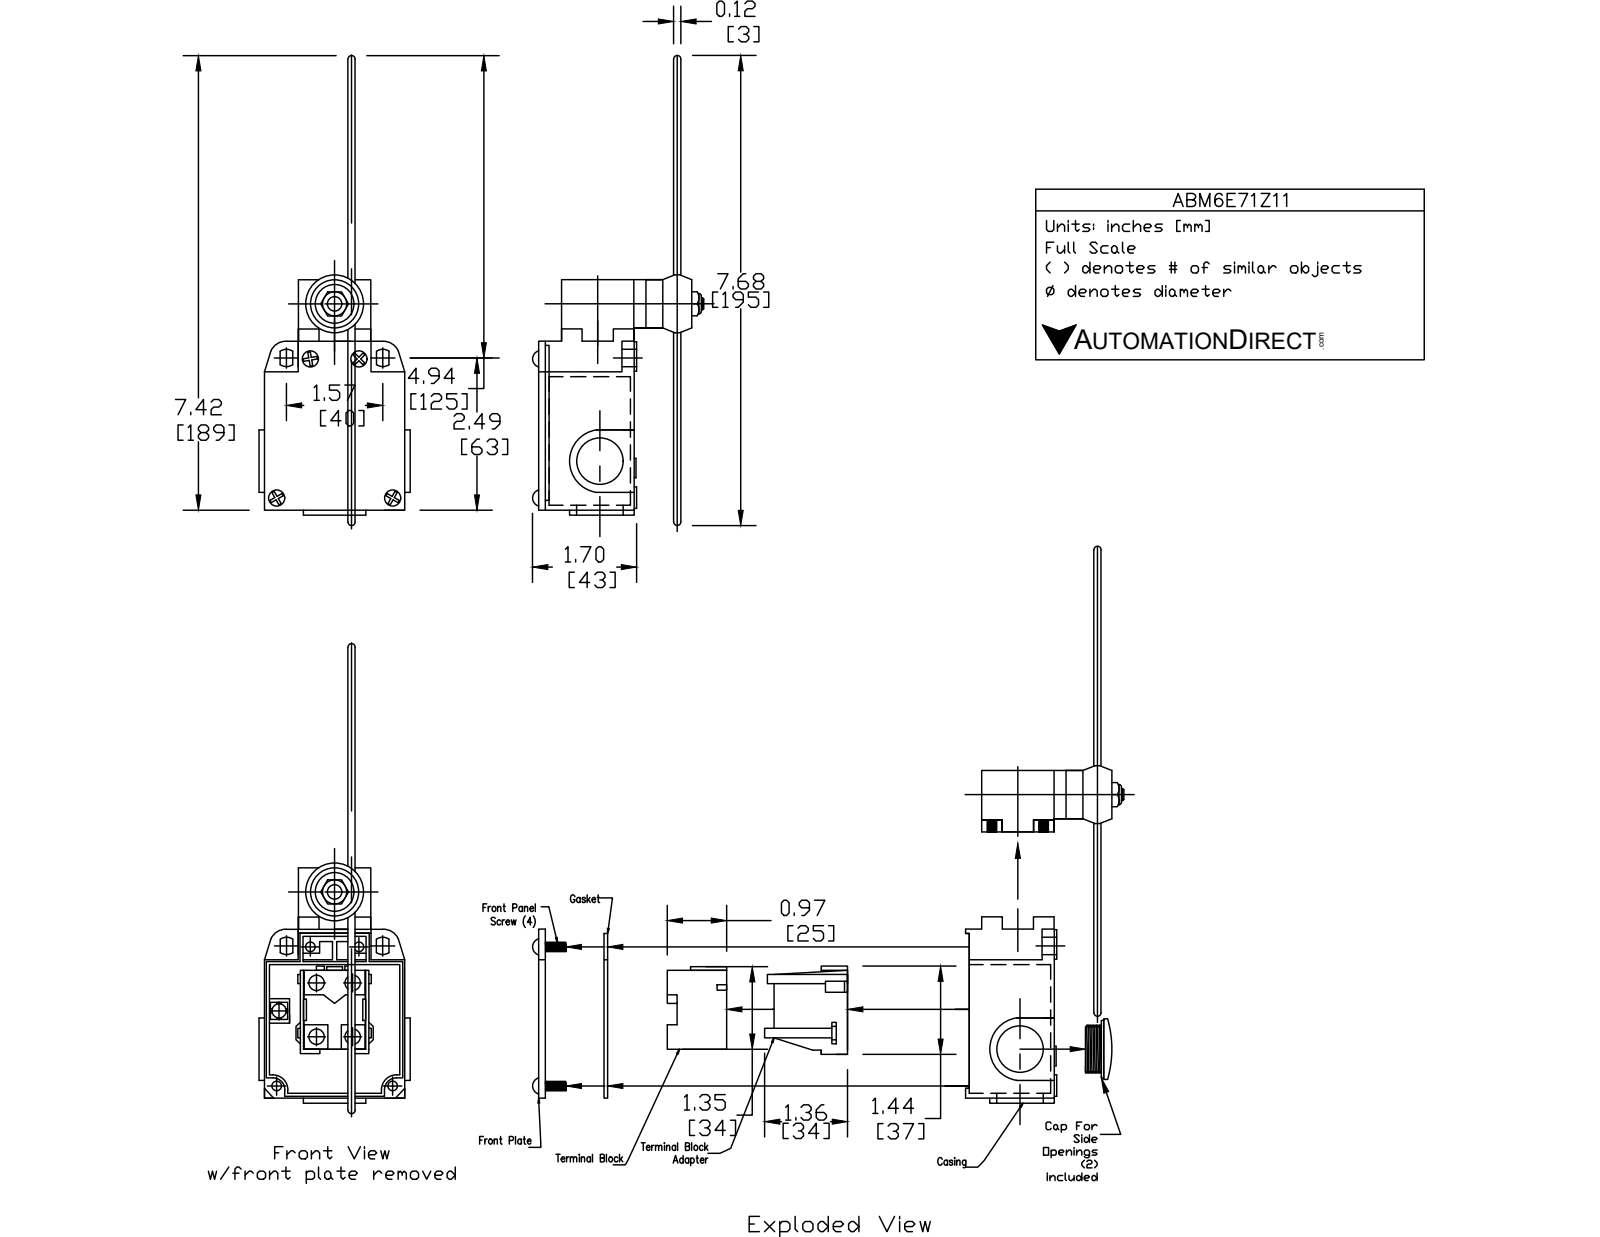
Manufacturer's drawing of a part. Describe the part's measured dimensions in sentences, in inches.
The part is named "ABM6E71Z11". Its 3-D file was written by "SolidWorks 2017 (AUTOMOTIVE_DESIGN)". It is 5 solids with 259 faces: 125 planar, 93 cylindrical and 41 other. Overall it measures 7.672 by 2.441 by 2.335 inches. Its volume is 10.98 cubic inches and its surface area 48.46 square inches. Round holes: 2 of diameter 0.669, 2 of diameter 0.748, 1 of diameter 0.118, 1 of diameter 0.236, 1 of diameter 0.551. Round bosses or shafts: 4 of diameter 0.276, 2 of diameter 0.472, 2 of diameter 0.354, 1 of diameter 0.945, 1 of diameter 0.787, 1 of diameter 0.394, 1 of diameter 0.236. Partial cylindrical surfaces (rounded edges, fillets, slot ends): 12 of radius 0.059, 4 of radius 0.039, 2 of radius 0.144, 2 of radius 0.256, 2 of radius 0.512, 1 of radius 0.453, 1 of radius 0.472. The main face-to-face distances are 1.555, 0.551, 1.732, 2.283, 0.079, 1.181, 0.236, 2.756, 0.512, 0.984. The hole center spacings are 1.394, 0.551.
